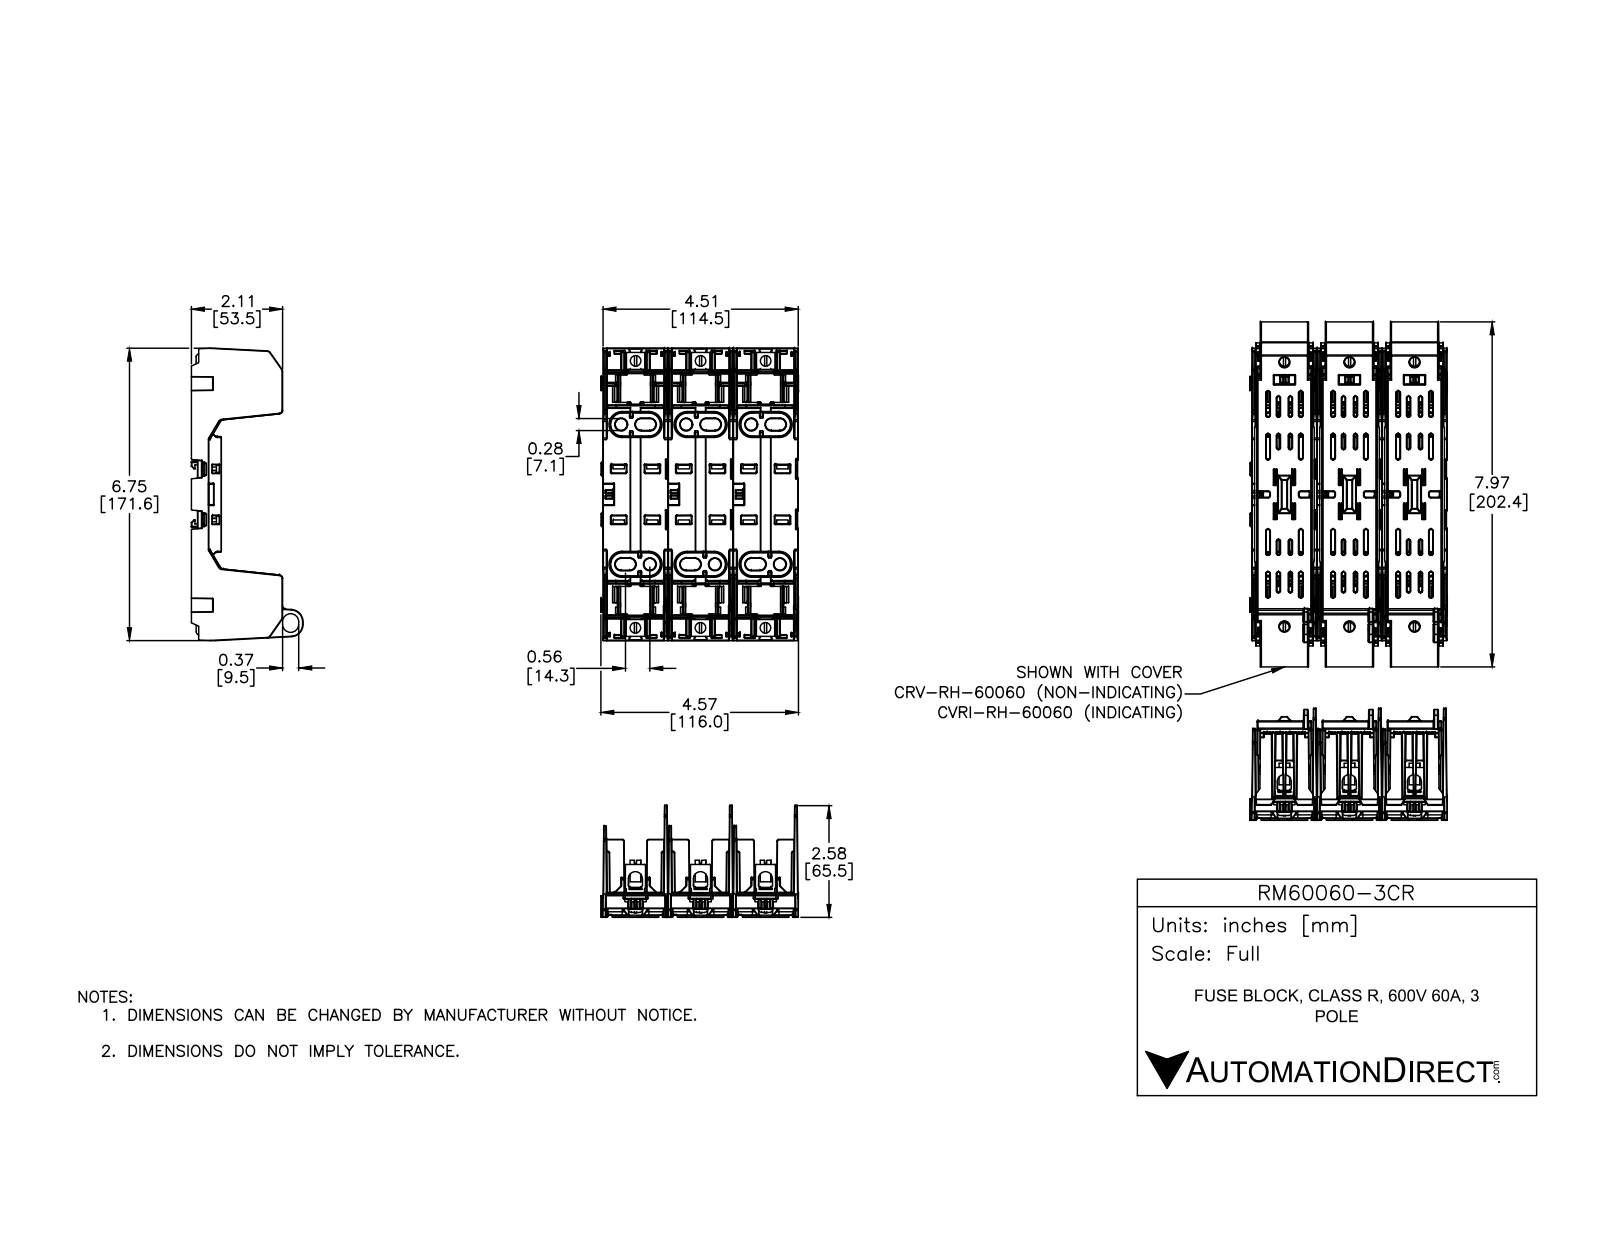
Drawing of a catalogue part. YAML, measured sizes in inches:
part_name: "RM60060-3CR"
step_written_by: "SolidWorks 2021 (CONFIG_CONTROL_DESIGN)"
units: inches
bodies: {solids: 21, faces: 2391, planar: 1401, cylindrical: 657, other: 333}
overall_size: [6.755, 4.567, 2.579]
volume: 15.42
surface_area: 231
round_holes:
  - {diameter: 0.244, count: 6}
  - {diameter: 0.278, count: 6}
round_bosses_or_shafts:
  - {diameter: 0.333, count: 6}
  - {diameter: 0.244, count: 6}
partial_cylinders:
  - {radius: 0.006, count: 105}
  - {radius: 0.012, count: 54}
  - {radius: 0.02, count: 48}
  - {radius: 0.039, count: 24}
  - {radius: 0.07, count: 12}
  - {radius: 0.079, count: 12}
  - {radius: 0.139, count: 12}
  - {radius: 0.276, count: 12}
face_to_face_distances: [1.504, 3.008, 1.506, 3.01, 0.202, 0.571, 0.369, 4.514, 1.502, 0.08]
hole_center_spacings: [1.504, 1.506, 4.708, 1.878, 2.352, 3.008, 4.842, 5.042]
